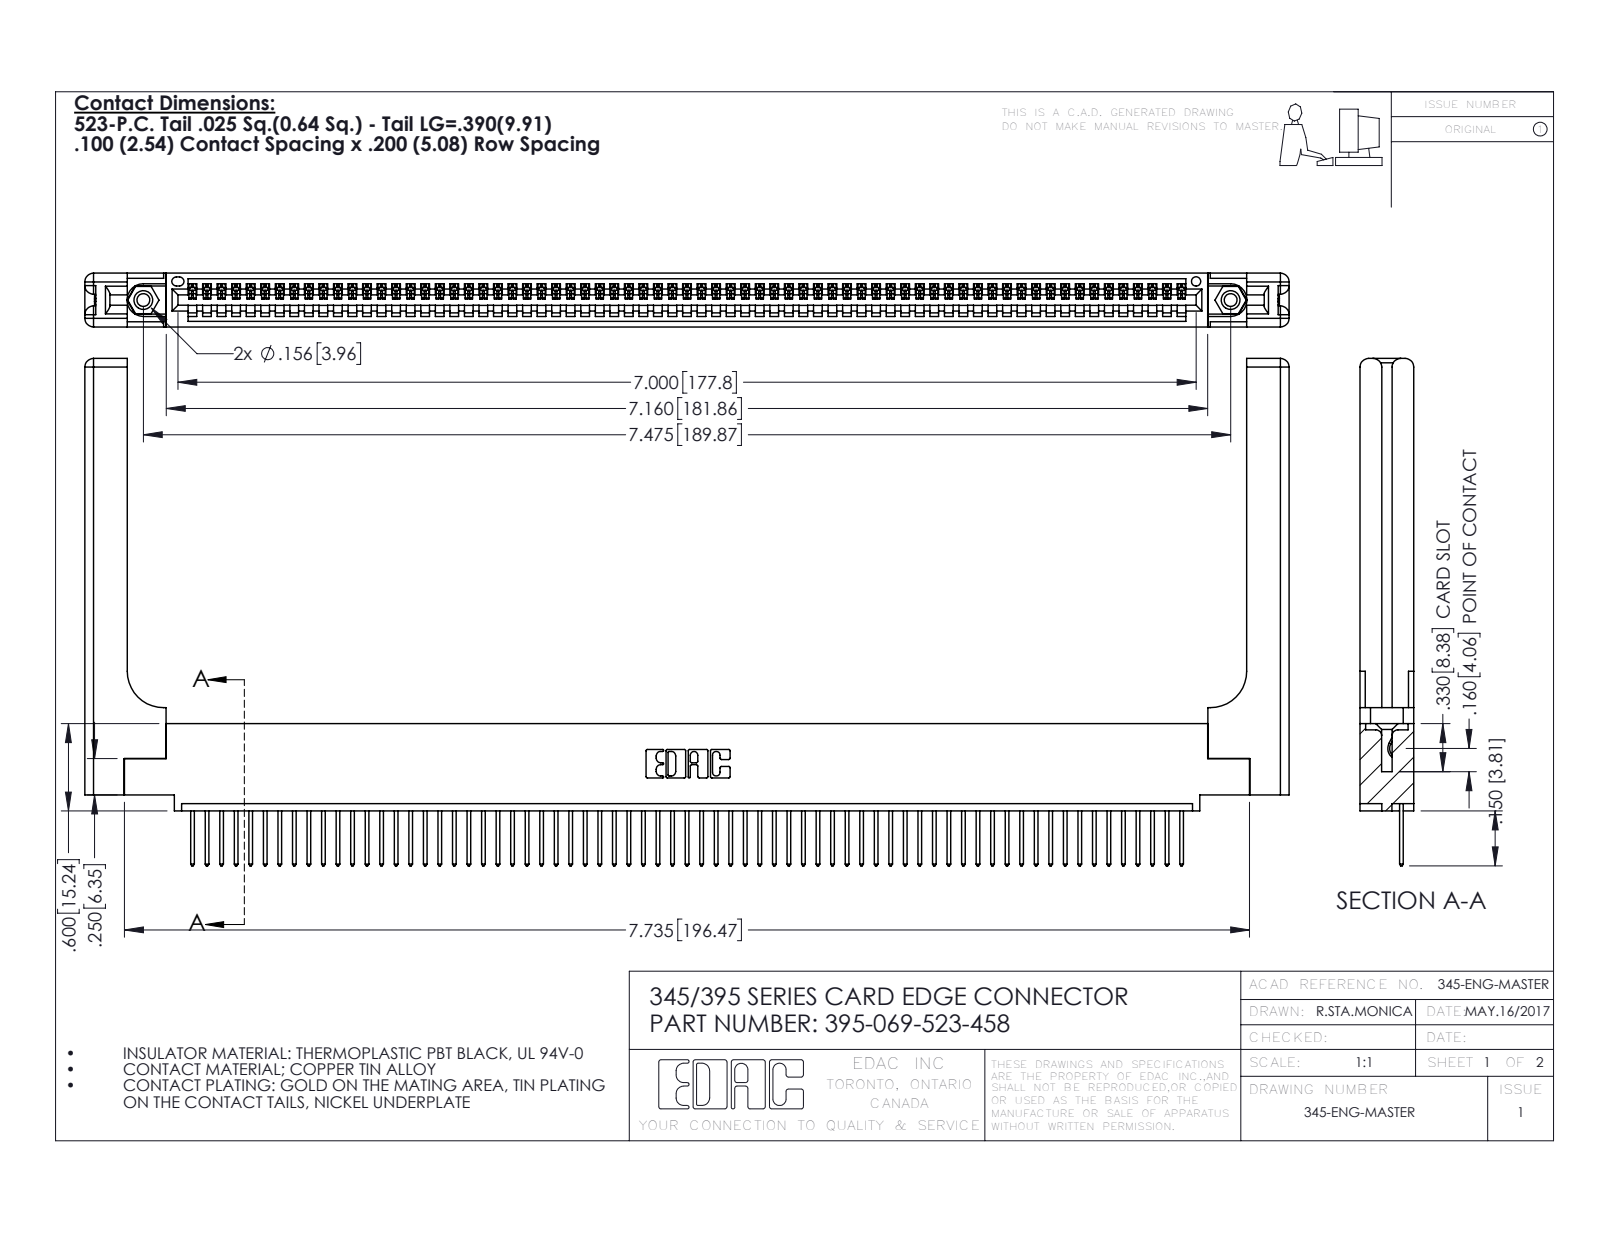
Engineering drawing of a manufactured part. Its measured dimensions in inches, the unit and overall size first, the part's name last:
Units: inches
Overall size (bounding box): 8.279 × 3.487 × 0.37
Round holes (diameter × count): ⌀0.089 ×2, ⌀0.125 ×2, ⌀0.156 ×2, ⌀0.064 ×1
Round bosses / shafts (diameter × count): ⌀0.155 ×2
Partial cylindrical surfaces — rounded edges, fillets, slot ends (radius × count): R0.006 ×138, R0.01 ×138, R0.01 ×22, R0.06 ×16, R0.007 ×6, R0.031 ×6, R0.026 ×3, R0.03 ×2
Main face-to-face distances: 0.072, 0.298, 0.37, 0.098, 0.272, 0.025, 0.2, 0.225, 0.148, 0.15
Hole centre spacings: 0.27, 7.239, 7.475
Volume: 1.745 in³ · Surface area: 50.43 in²
Bodies: 74 solids, 4388 faces (2992 planar, 1336 cylindrical, 60 other)
Part name (STEP PRODUCT): 345 Part_0.110 Offset - 0.156 Dia-TH; 345-250-001_345-250-001-102; 395-069-523-458; 345-292-001_345-293-123 (+1 more)
STEP written by: SolidWorks 2016 (CONFIG_CONTROL_DESIGN)
